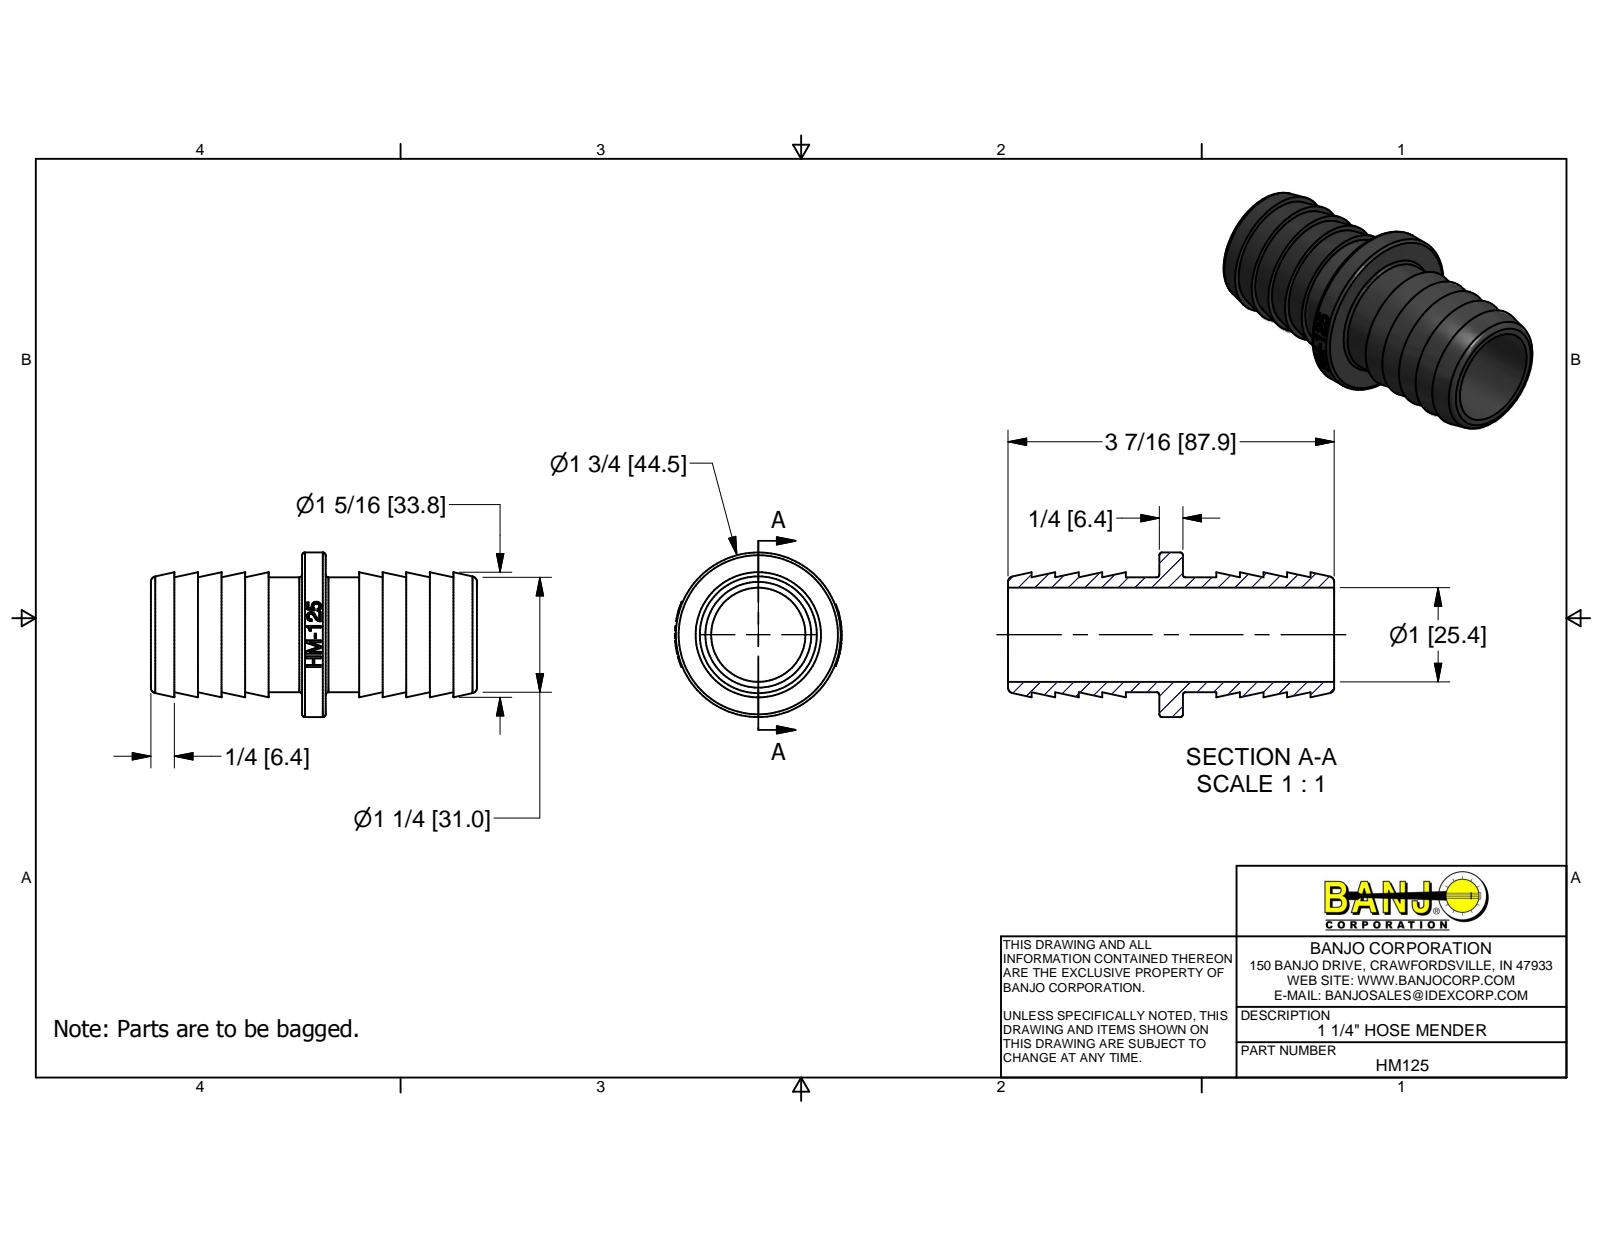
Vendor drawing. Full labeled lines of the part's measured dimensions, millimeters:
Part name (STEP PRODUCT): HM125
STEP written by: Autodesk Inventor 2014 (AUTOMOTIVE_DESIGN)
Units: millimetres
Bodies: 1 solid, 184 faces (82 planar, 19 cylindrical, 83 other)
Overall size (bounding box): 87.88 × 44.96 × 44.45
Volume: 31 207 mm³ · Surface area: 19 601 mm²
Round holes (diameter × count): ⌀25.4 ×1
Round bosses / shafts (diameter × count): ⌀44.45 ×1, ⌀30.99 ×1
Partial cylindrical surfaces — rounded edges, fillets, slot ends (radius × count): R22.48 ×1
Main face-to-face distances: 6.35, 12.7, 19.05, 56.14, 49.79, 62.49, 34.42, 28.07, 21.72, 15.37
